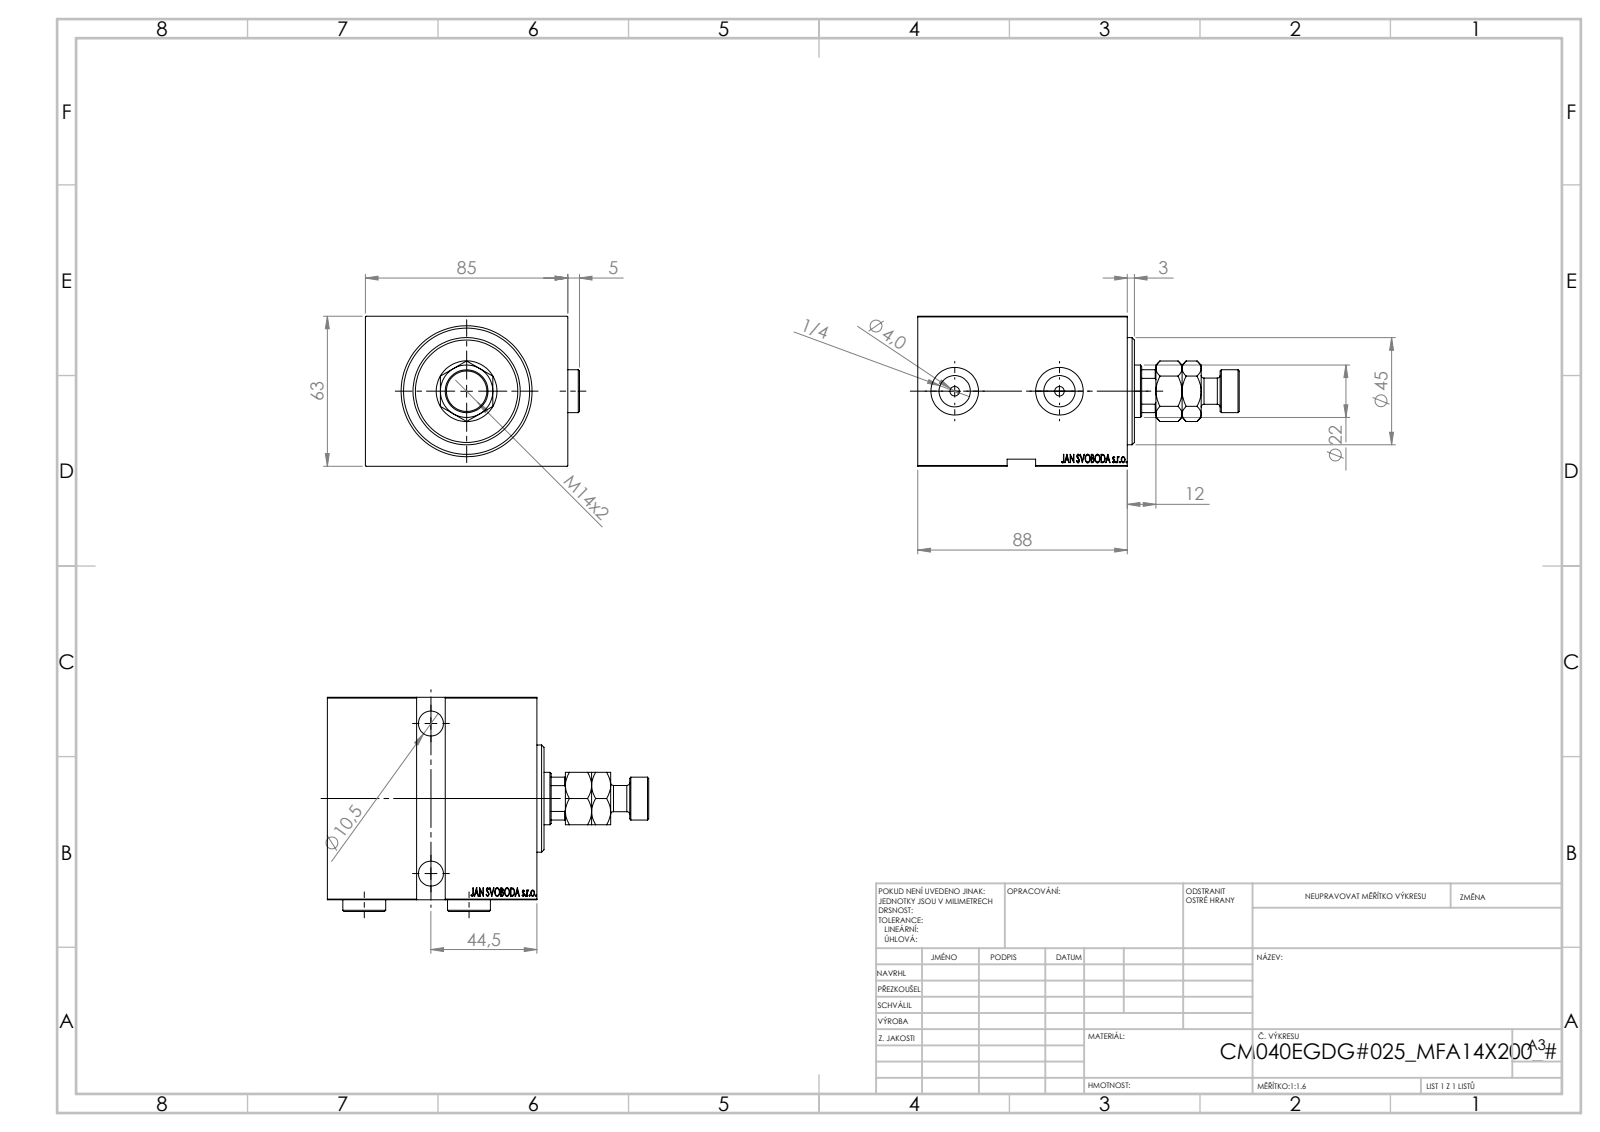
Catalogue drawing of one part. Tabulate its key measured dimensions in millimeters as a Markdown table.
| quantity | value |
| --- | --- |
| part name | MFA; V450CM_VC_B; Zatka_OIL_PORT; V450CM_E_Body (+1 more) |
| STEP written by | SolidWorks 2019 (CONFIG_CONTROL_DESIGN) |
| units | millimeters |
| bodies | 6 solids, 954 faces (460 planar, 64 cylindrical, 430 other) |
| overall size | 135 × 89.9 × 63 |
| volume | 447 306 mm³ |
| surface area | 77 879 mm² |
| round holes (diameter × count) | 4 × 2, 10.5 × 2, 13.16 × 2, 16.5 × 2, 20 × 2, 12.5 × 1, 22 × 1, 25.5 × 1, 40 × 1, 53 × 1 |
| round bosses / shafts (diameter × count) | 18 × 3, 45 × 1, 42 × 1, 11 × 1 |
| partial cylindrical surfaces (radius × count) | 10.5 × 1 |
| main face-to-face distances | 63, 85, 88, 12, 76, 5, 3, 71, 83, 84.9 |
| hole center spacings | 44, 63 |
